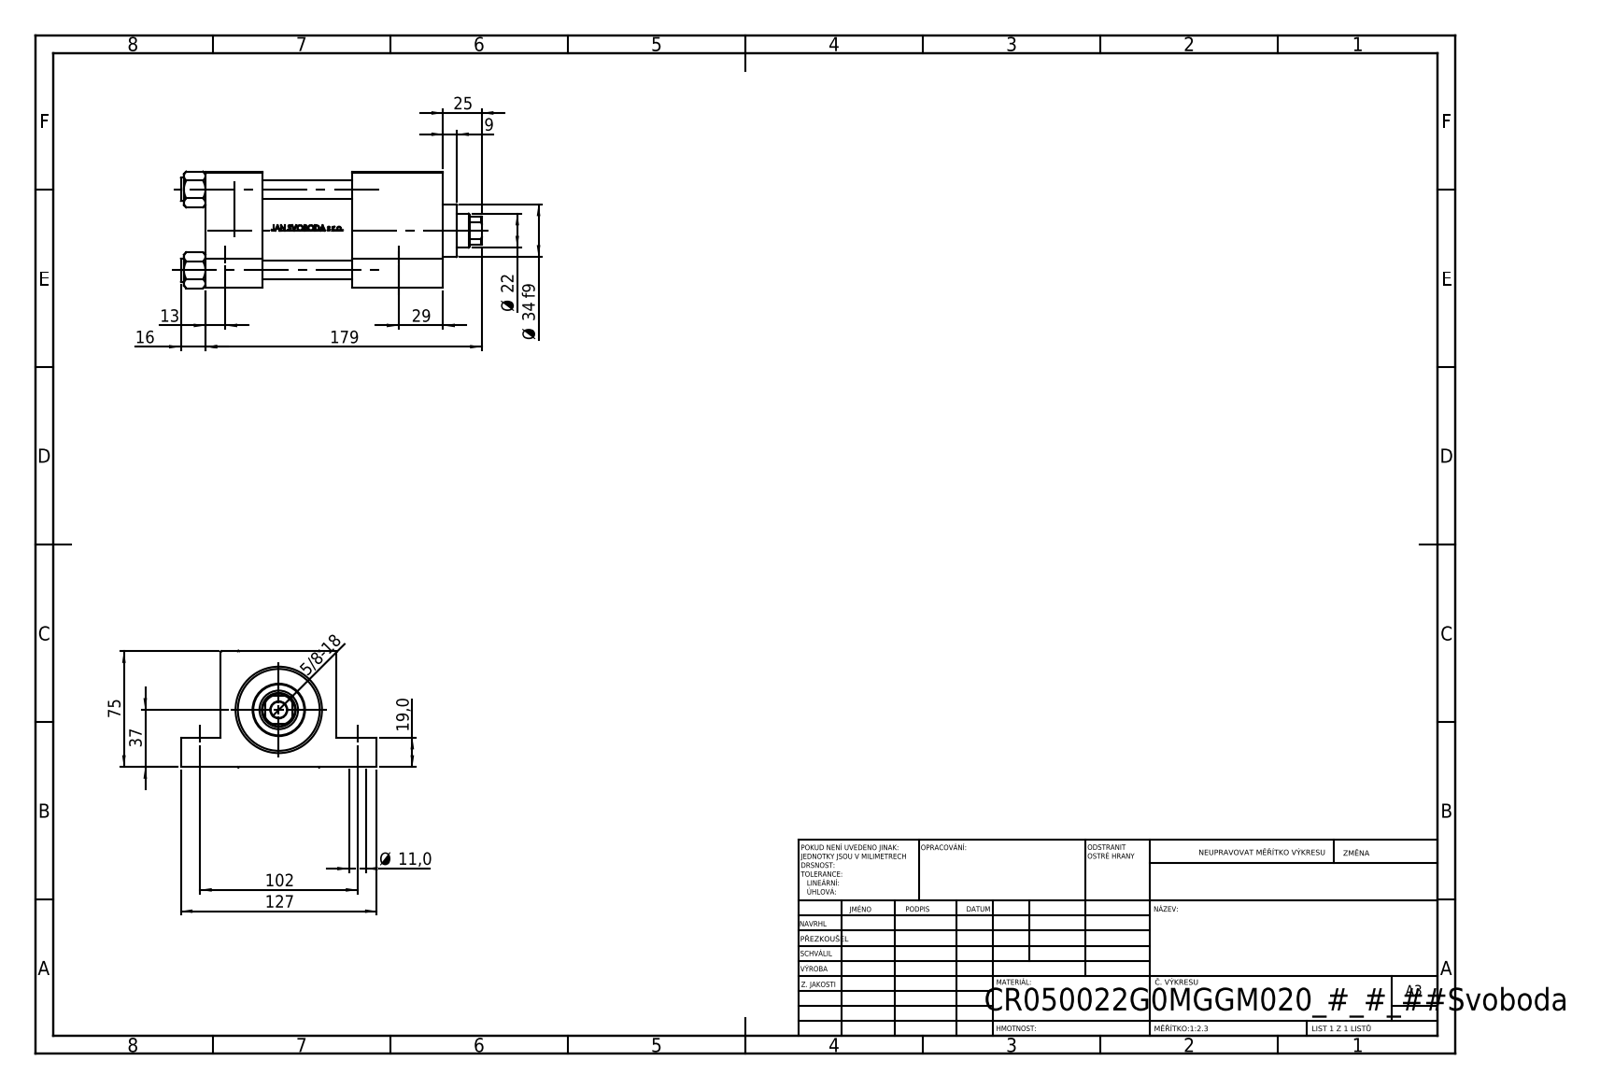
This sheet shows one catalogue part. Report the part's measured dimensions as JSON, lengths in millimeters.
{"part_name": "V215CR_G_Body; V215CR_G_TYCINKA; NUT_M5_G; V215CR_VCP_G (+1 more)", "step_written_by": "SolidWorks 2019 (CONFIG_CONTROL_DESIGN)", "units": "millimeters", "bodies": {"solids": 11, "faces": 1088, "planar": 432, "cylindrical": 124, "other": 532}, "overall_size": [195, 127, 75.54], "volume_mm3": 755753, "surface_area_mm2": 159364, "round_holes": [[12, 4], [11, 3], [7, 2], [20.96, 2], [30, 2], [10.5, 1], [11, 1], [22, 1], [25, 1], [41, 1], [50, 1], [53, 1]], "round_bosses_or_shafts": [[15, 4], [56, 1], [34, 1]], "partial_cylinders_radius": [[10.5, 1]], "face_to_face_distances": [75, 37, 154, 117, 19, 56, 95, 58, 59, 26], "hole_center_spacings": [52.3, 36.63, 37.34, 51.3, 52.63, 73.96, 102, 111.36]}
